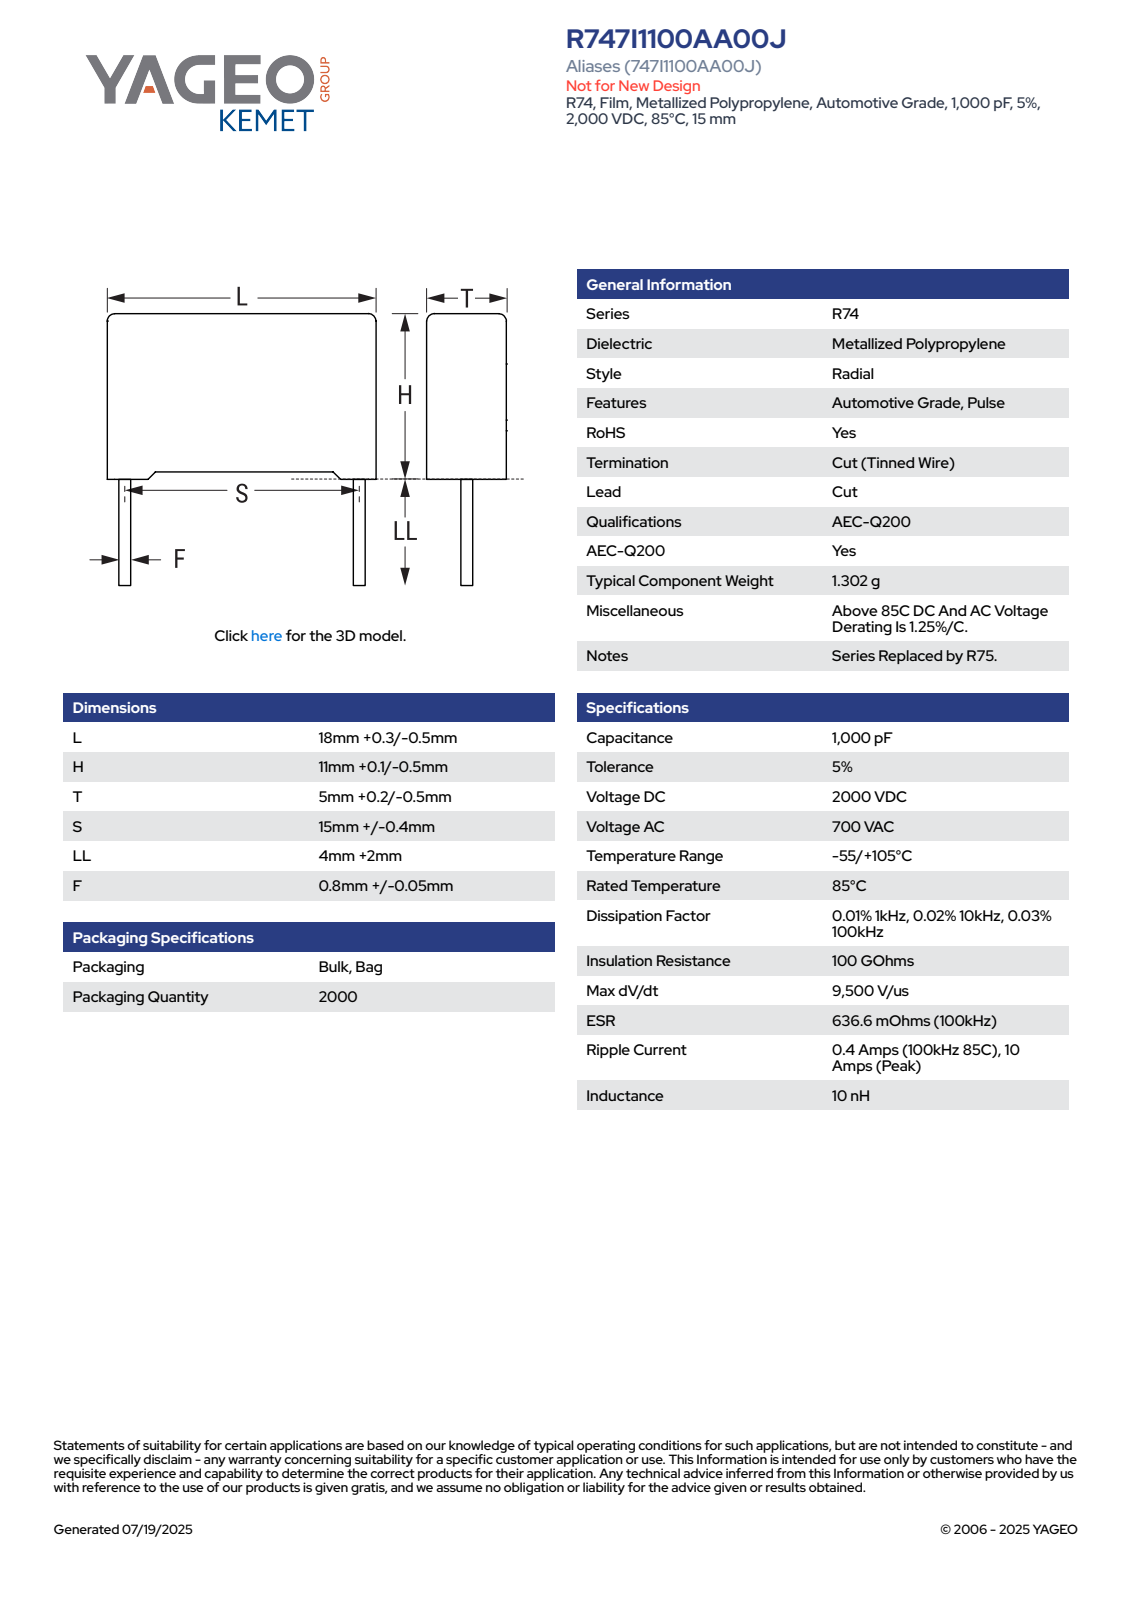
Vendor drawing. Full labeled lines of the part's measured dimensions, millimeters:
Part name (STEP PRODUCT): CFR_RB2_18X11X5_L18.3H11.1T5.2S15LL6F0.85
STEP written by: SolidWorks 2021 (AUTOMOTIVE_DESIGN)
Units: millimetres
Bodies: 4 solids, 85 faces (77 planar, 8 cylindrical, 0 other)
Overall size (bounding box): 18.3 × 17.1 × 5.21
Volume: 1 005 mm³ · Surface area: 777 mm²
Round bosses / shafts (diameter × count): ⌀0.85 ×2
Partial cylindrical surfaces — rounded edges, fillets, slot ends (radius × count): R0.5 ×4
Main face-to-face distances: 5.2, 10.35, 18.3, 0.61, 4.59, 0.37, 10.72, 0.38, 0.75, 11.1
